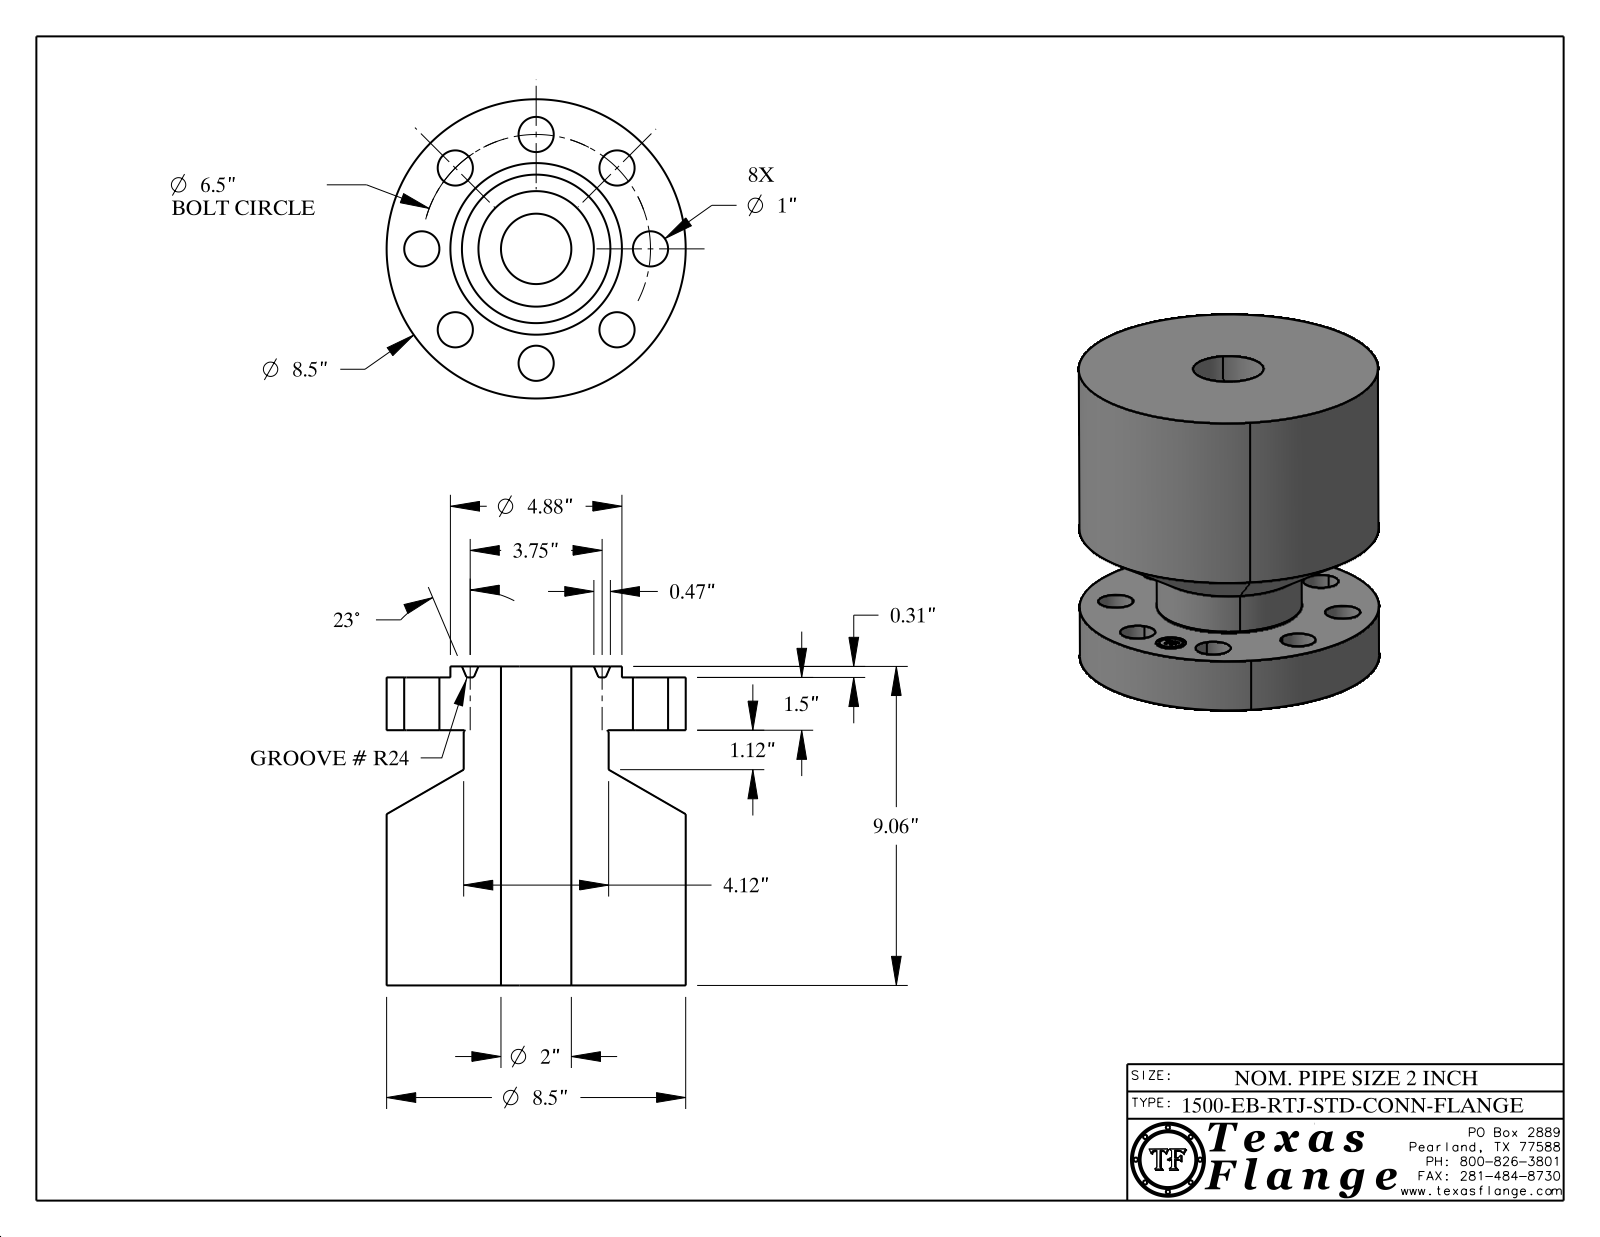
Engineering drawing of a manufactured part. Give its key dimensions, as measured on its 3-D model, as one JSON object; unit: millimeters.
{"part_name": "2-1500-EB-RTJ-STD-CONN-FLANGE", "step_written_by": "CATIA V5 STEP AP214 (AUTOMOTIVE_DESIGN)", "units": "millimeters", "bodies": {"solids": 1, "faces": 431, "planar": 371, "cylindrical": 46, "other": 14}, "overall_size": [230.2, 215.9, 215.9], "volume_mm3": 6293000, "surface_area_mm2": 308000, "round_holes": [[25.4, 8], [21.6, 1], [50.8, 1]], "round_bosses_or_shafts": [[1.3, 8], [215.9, 1], [123.8, 1], [104.6, 1], [17, 1]], "face_to_face_distances": [184.2, 38.1, 222.3, 8, 46.1, 230.2, 45.9, 38, 184.3, 6.5], "hole_center_spacings": [82.6, 63.2, 116.7, 152.5, 165.1, 32.2, 137.3, 161.9]}
